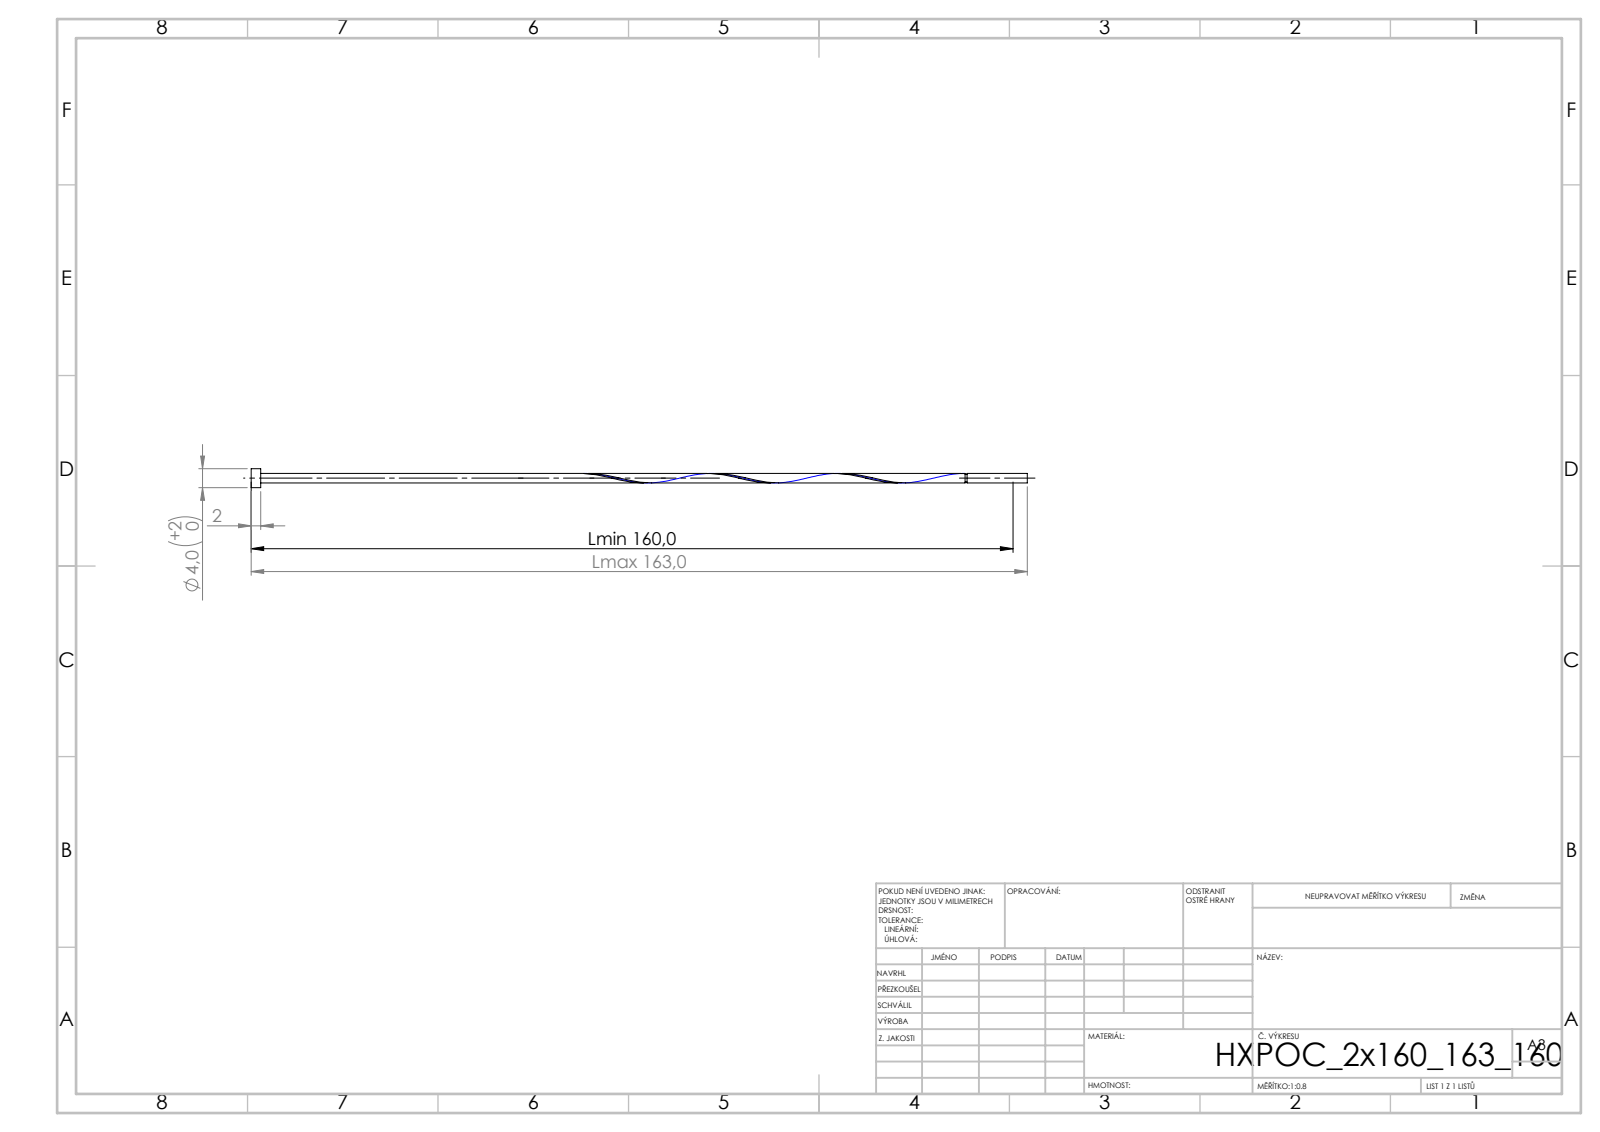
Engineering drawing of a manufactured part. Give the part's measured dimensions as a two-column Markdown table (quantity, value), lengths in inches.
| quantity | value |
| --- | --- |
| STEP written by | SolidWorks 2019 (CONFIG_CONTROL_DESIGN) |
| units | inches |
| bodies | 1 solid, 16 faces (6 planar, 9 cylindrical, 1 other) |
| overall size | 6.417 × 0.157 × 0.157 |
| volume | 0.039 in³ |
| surface area | 2.192 in² |
| round bosses / shafts (diameter × count) | 0.157 × 1, 0.079 × 1, 0.063 × 1 |
| main face-to-face distances | 0.079, 6.417, 6.339, 5.919, 5.84, 0.498, 5.903, 5.824, 0.016, 0.514 |
